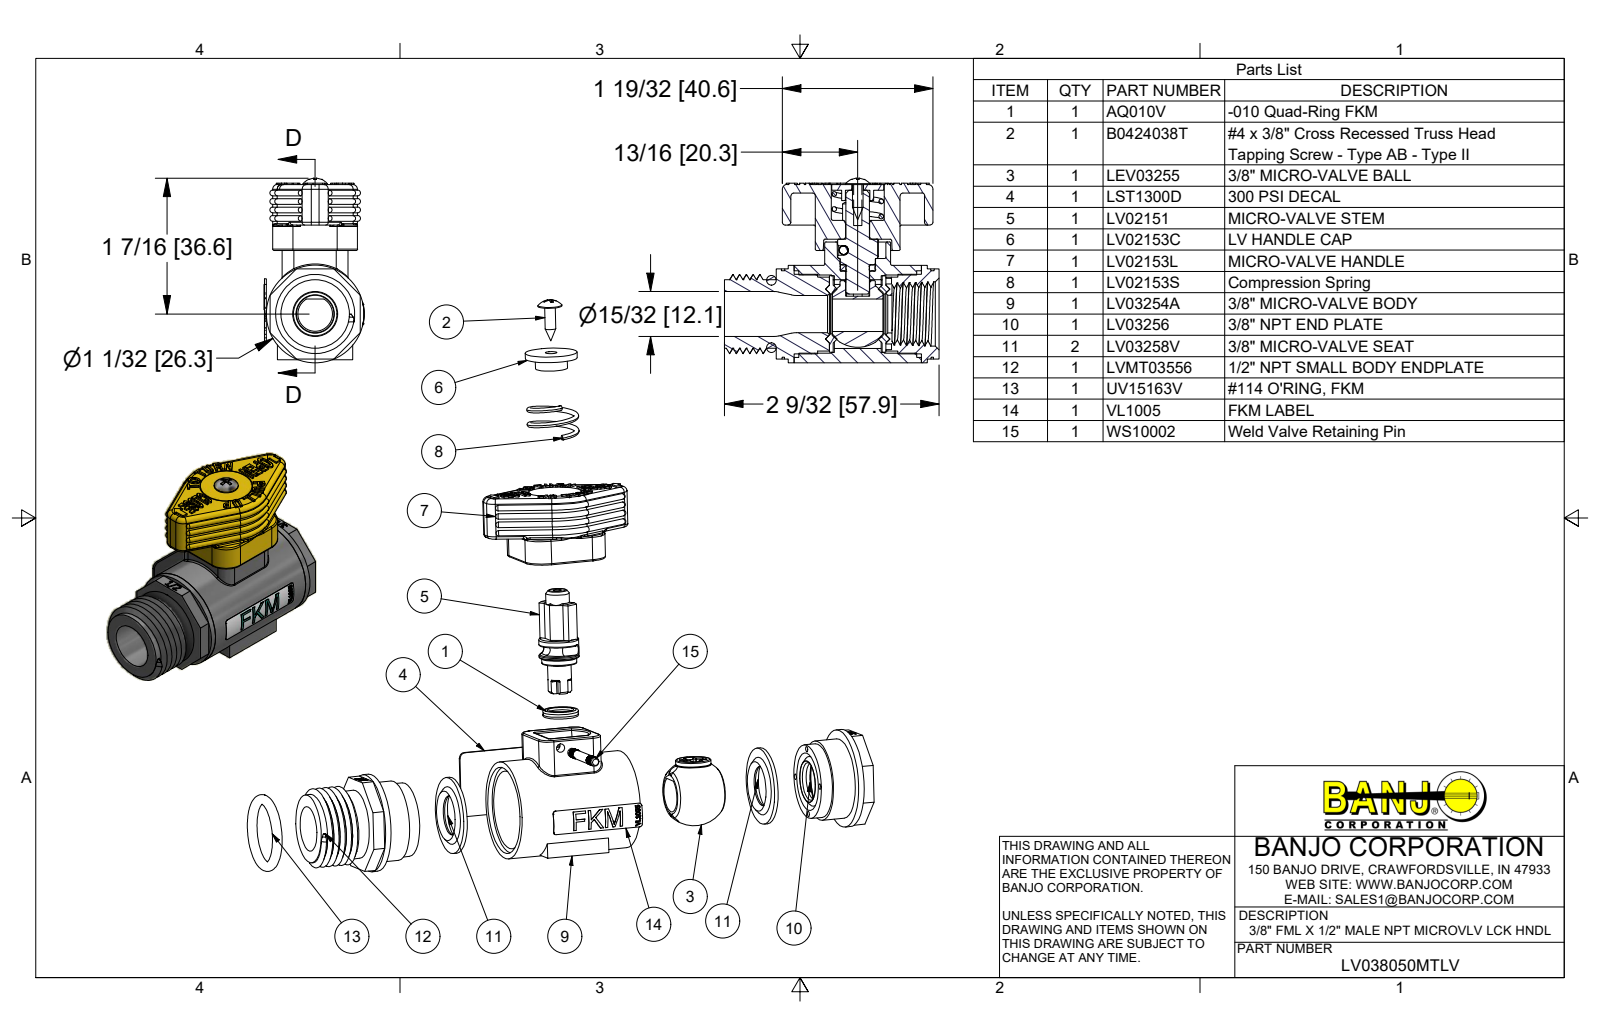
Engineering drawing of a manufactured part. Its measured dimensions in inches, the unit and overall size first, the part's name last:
Units: inches
Overall size (bounding box): 10.98 × 1.96 × 1.063
Round holes (diameter × count): ⌀0.06 ×4, ⌀0.089 ×1, ⌀0.093 ×1, ⌀0.125 ×1, ⌀0.181 ×1, ⌀0.251 ×1, ⌀0.257 ×1, ⌀0.26 ×1, ⌀0.366 ×1, ⌀0.37 ×1, ⌀0.376 ×1, ⌀0.395 ×1
Round bosses / shafts (diameter × count): ⌀1.035 ×1, ⌀0.845 ×1, ⌀0.812 ×1, ⌀0.785 ×1, ⌀0.726 ×1, ⌀0.552 ×1, ⌀0.425 ×1, ⌀0.375 ×1
Partial cylindrical surfaces — rounded edges, fillets, slot ends (radius × count): R0.03 ×40, R0.015 ×36, R0.01 ×16, R0.05 ×8, R0.06 ×4, R0.109 ×4, R0.125 ×4, R0.215 ×4
Main face-to-face distances: 0.977, 0.05, 0.377, 0.09, 0.75, 0.8, 0.02, 0.188, 0.565, 1.165
Hole centre spacings: 0.35, 0.494, 0.699, 0.541
Volume: 1.892 in³ · Surface area: 61.82 in²
Bodies: 16 solids, 3540 faces (2353 planar, 255 cylindrical, 932 other)
Part name (STEP PRODUCT): LV038050MTLV; LV03258V; LV03256; LVMT03556 (+8 more)
STEP written by: Autodesk Inventor 2018 (AUTOMOTIVE_DESIGN)
